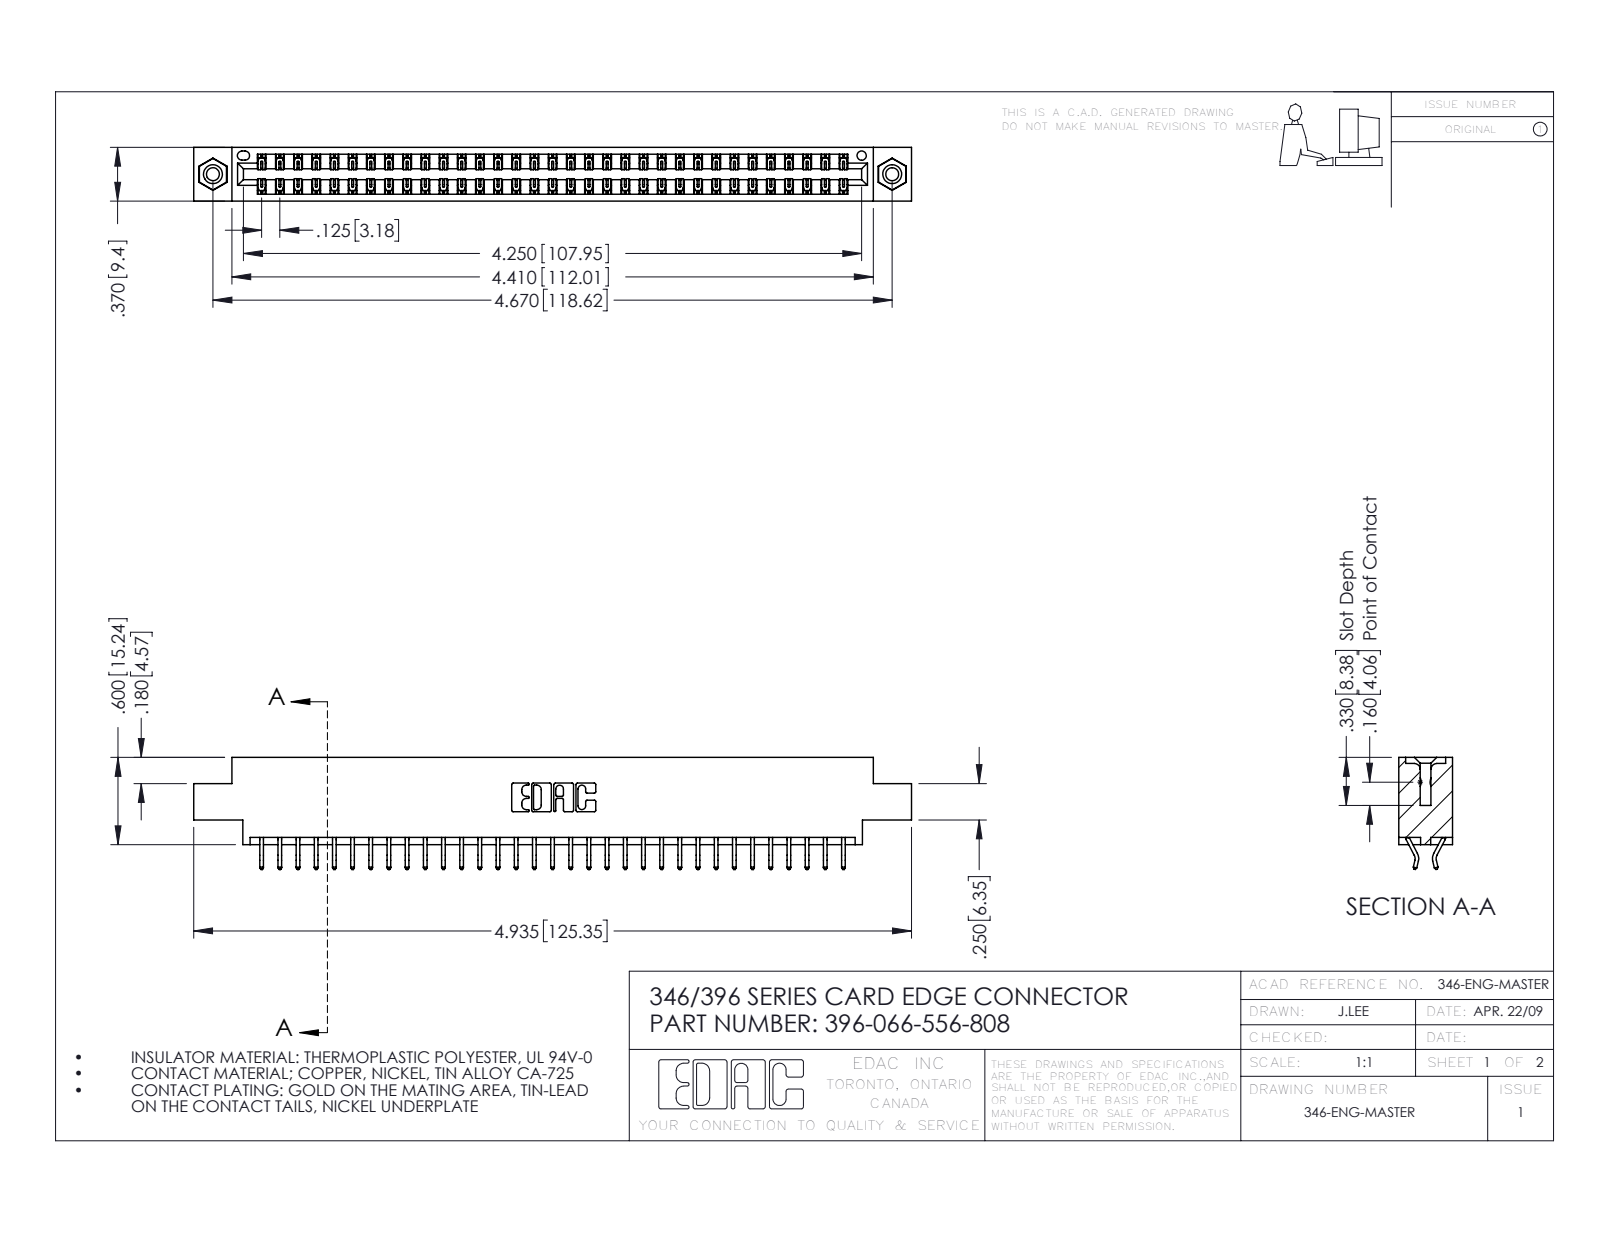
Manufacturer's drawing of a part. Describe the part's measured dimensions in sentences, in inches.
The part is named "396-066-556-808; 346 Part_0.170 Offset - 0.156 Dia-TI; 345-292-001_556 Tail; 345-250-001_345-250-003-102". Its 3-D file was written by "SolidWorks 2016 (CONFIG_CONTROL_DESIGN)". It is 69 solids with 4014 faces: 2686 planar, 1312 cylindrical and 16 other. Overall it measures 4.935 by 0.77 by 0.37 inches. Its volume is 0.732 cubic inches and its surface area 25.54 square inches. Round holes: 2 of diameter 0.089, 2 of diameter 0.125, 2 of diameter 0.156, 1 of diameter 0.064. Round bosses or shafts: 2 of diameter 0.155. Partial cylindrical surfaces (rounded edges, fillets, slot ends): 99 of radius 0.006, 22 of radius 0.01, 6 of radius 0.007, 6 of radius 0.031, 3 of radius 0.026, 2 of radius 0.01, 2 of radius 0.014, 2 of radius 0.022. The main face-to-face distances are 0.048, 0.322, 0.37, 0.25, 0.025, 0.072, 0.298, 0.275, 0.222, 0.148. The hole center spacings are 0.246, 4.462, 4.67.
